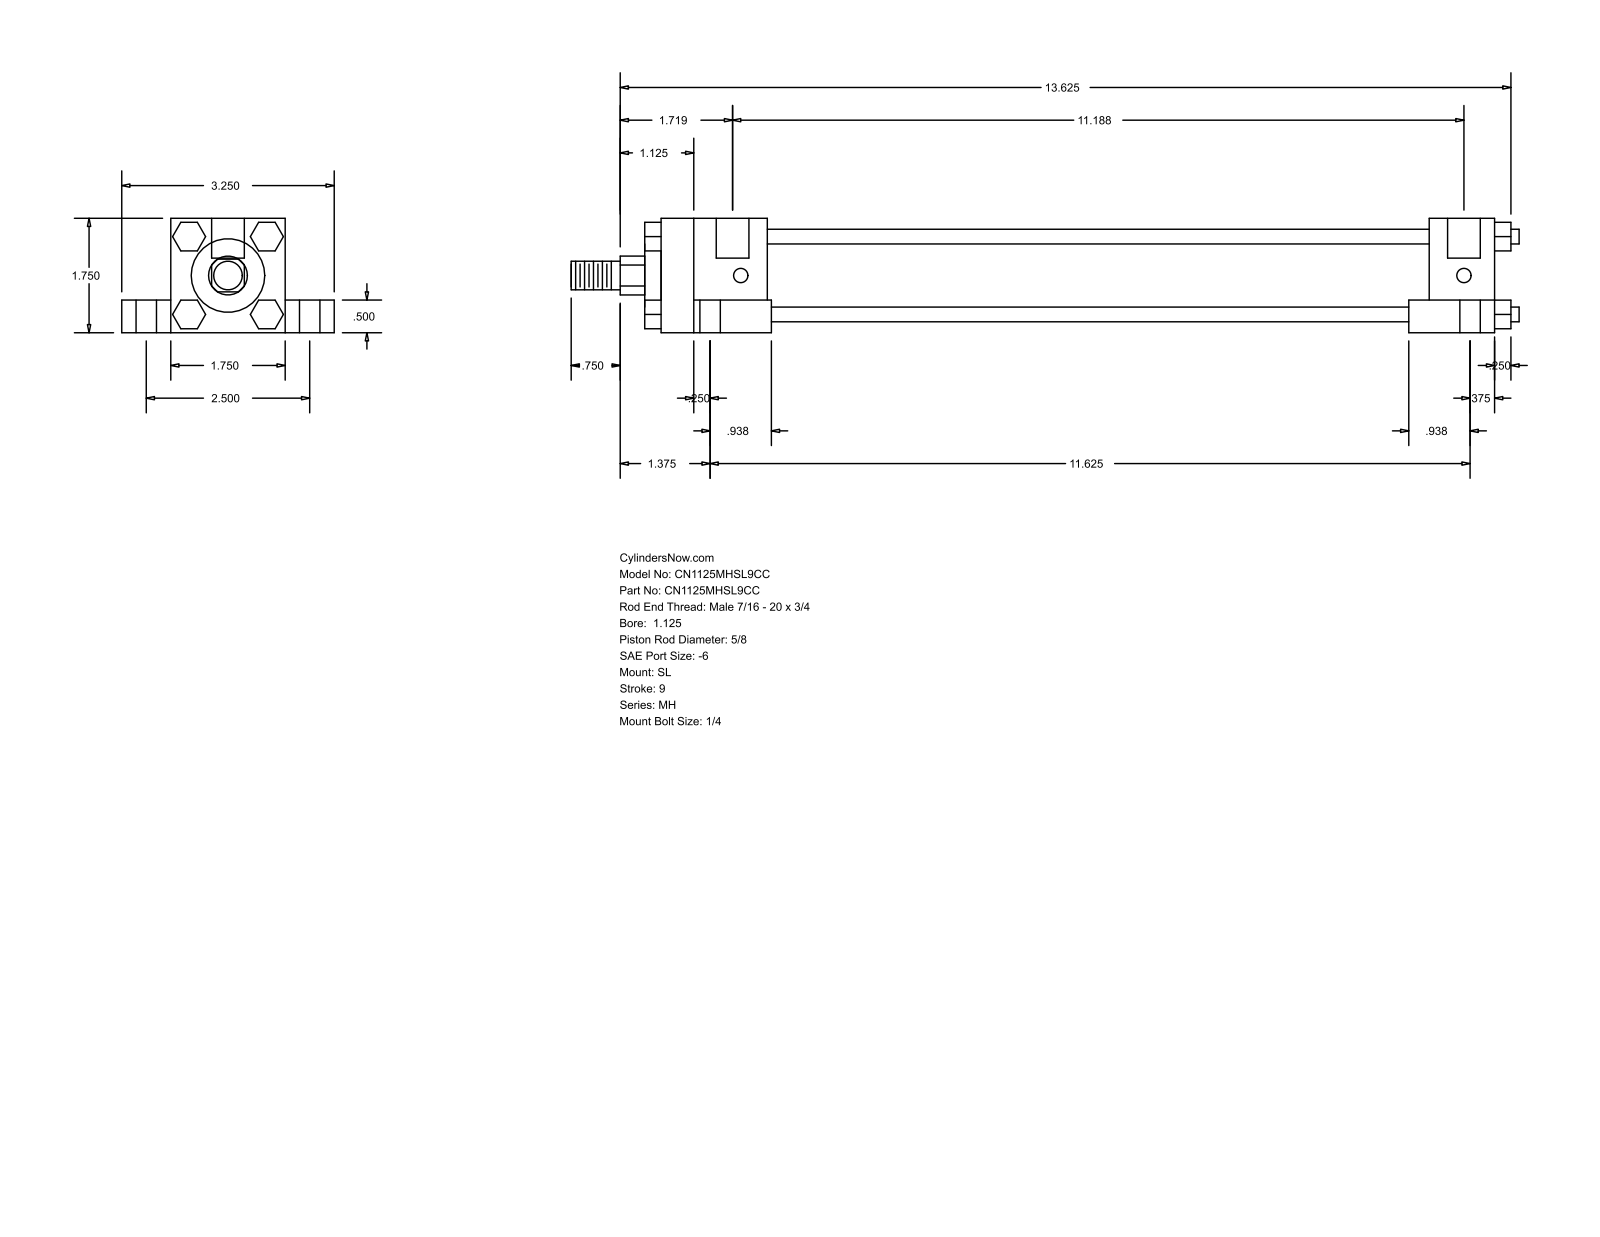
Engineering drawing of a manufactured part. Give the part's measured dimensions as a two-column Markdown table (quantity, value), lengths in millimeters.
| quantity | value |
| --- | --- |
| part name | MH_SL__0112_0.625 |
| STEP written by | GSSL Pune (CONFIG_CONTROL_DESIGN) |
| units | millimeters |
| bodies | 0 solids, 150 faces (114 planar, 36 cylindrical, 0 other) |
| overall size | 368.3 × 82.55 × 44.45 |
| round holes (diameter × count) | 5.56 × 4, 7.94 × 4, 14.29 × 4, 12.7 × 2 |
| round bosses / shafts (diameter × count) | 5.71 × 4, 34.92 × 1, 28.57 × 1, 15.88 × 1, 11.11 × 1 |
| partial cylindrical surfaces (radius × count) | 7.54 × 1 |
| main face-to-face distances | 44.46, 19.04, 12.7, 31.76, 63.5, 11.11, 47.62, 33.34, 277.82, 257.17 |
| hole center spacings | 31.84, 32.23, 32.93, 63.5, 280.99, 285.14, 288.29, 291.45 |
